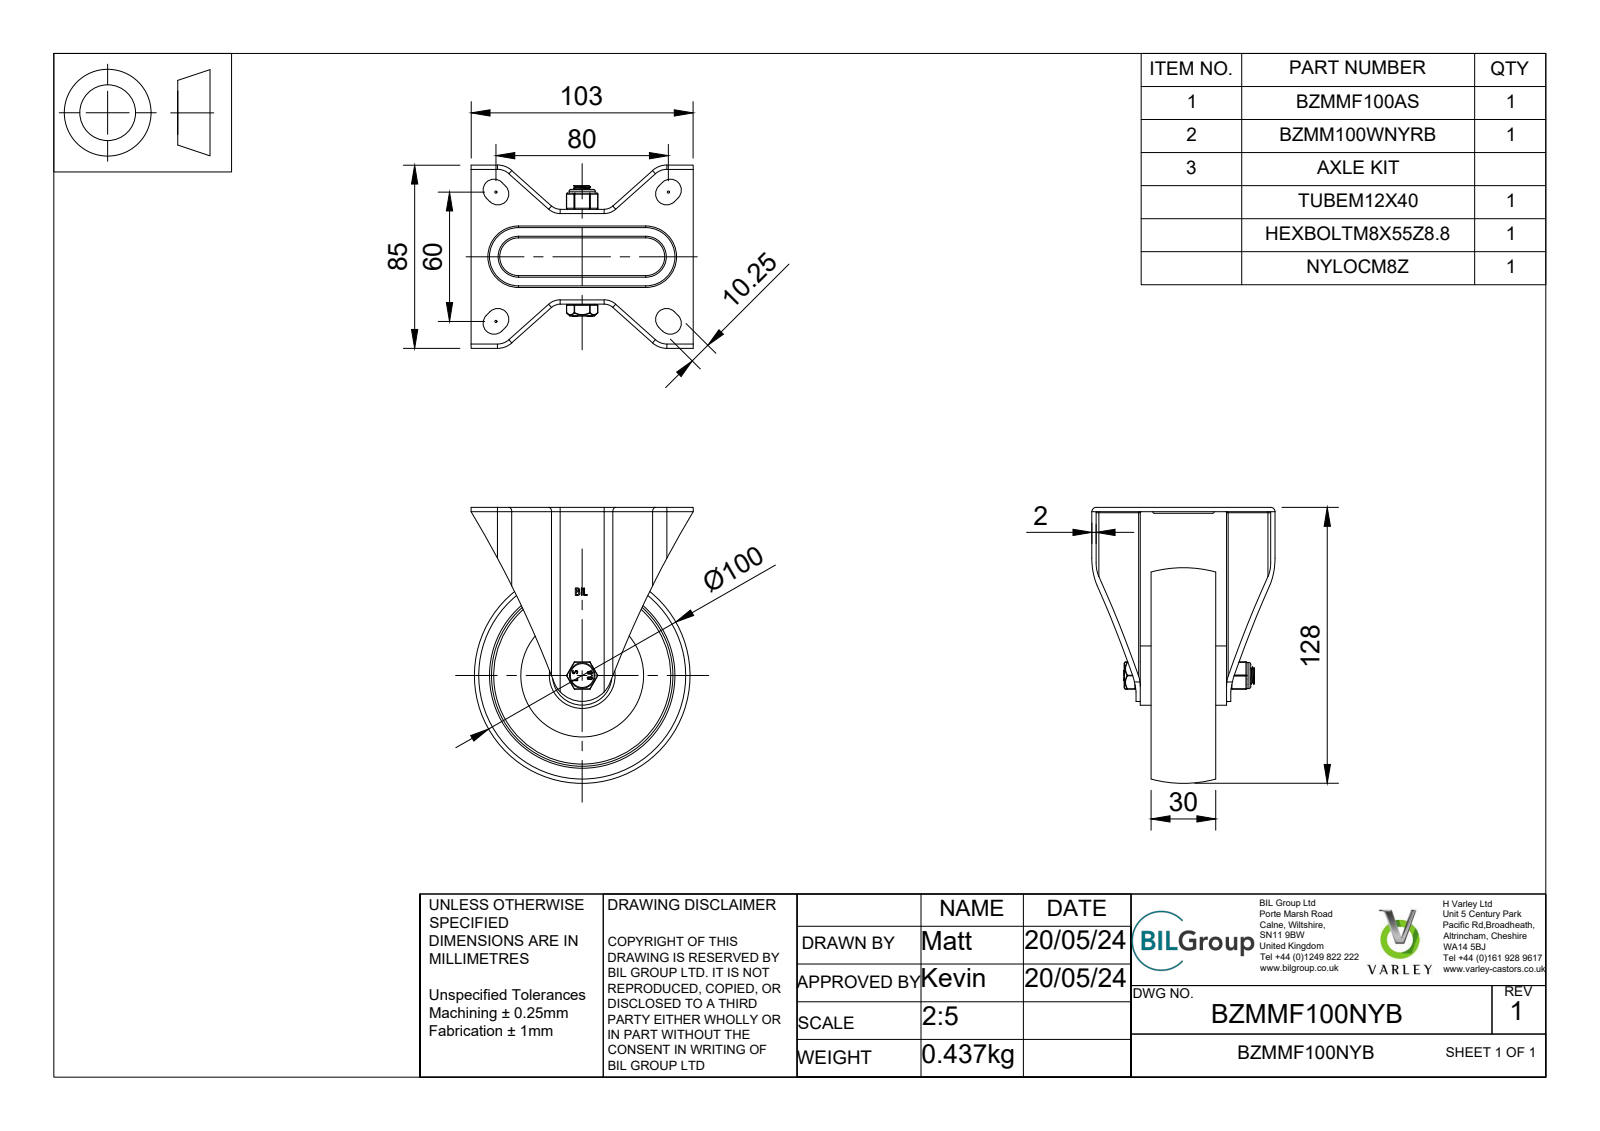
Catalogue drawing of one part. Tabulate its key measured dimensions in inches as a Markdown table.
| quantity | value |
| --- | --- |
| part name | BZMMF100NYB v3; BZMMF100AS v1; BZMMF100AS; ZINC PLATED, PRESSED STEEL BRACKET (+7 more) |
| STEP written by | Autodesk Translation Framework v13.14.0.145 (AUTOMOTIVE_DESIGN) |
| units | inches |
| bodies | 16 solids, 497 faces (192 planar, 207 cylindrical, 98 other) |
| overall size | 5.039 × 4.055 × 3.346 |
| volume | 9.743 in³ |
| surface area | 131.8 in² |
| round holes (diameter × count) | 0.026 × 2, 0.315 × 1, 0.325 × 1, 0.331 × 1, 0.339 × 1, 0.48 × 1, 0.492 × 1, 0.787 × 1 |
| round bosses / shafts (diameter × count) | 0.148 × 8, 1.083 × 1, 0.768 × 1, 0.476 × 1, 0.469 × 1, 0.453 × 1, 0.31 × 1, 0.254 × 1 |
| partial cylindrical surfaces (radius × count) | 0.02 × 26, 0.01 × 12, 0.03 × 8, 0.079 × 8, 0.202 × 8, 0.013 × 4, 0.025 × 4, 0.118 × 4 |
| main face-to-face distances | 0.079, 0.561, 0.935, 0.64, 0.719, 1.014, 1.654, 1.378, 0.483, 0.276 |
| hole center spacings | 0.127, 0.098 |
